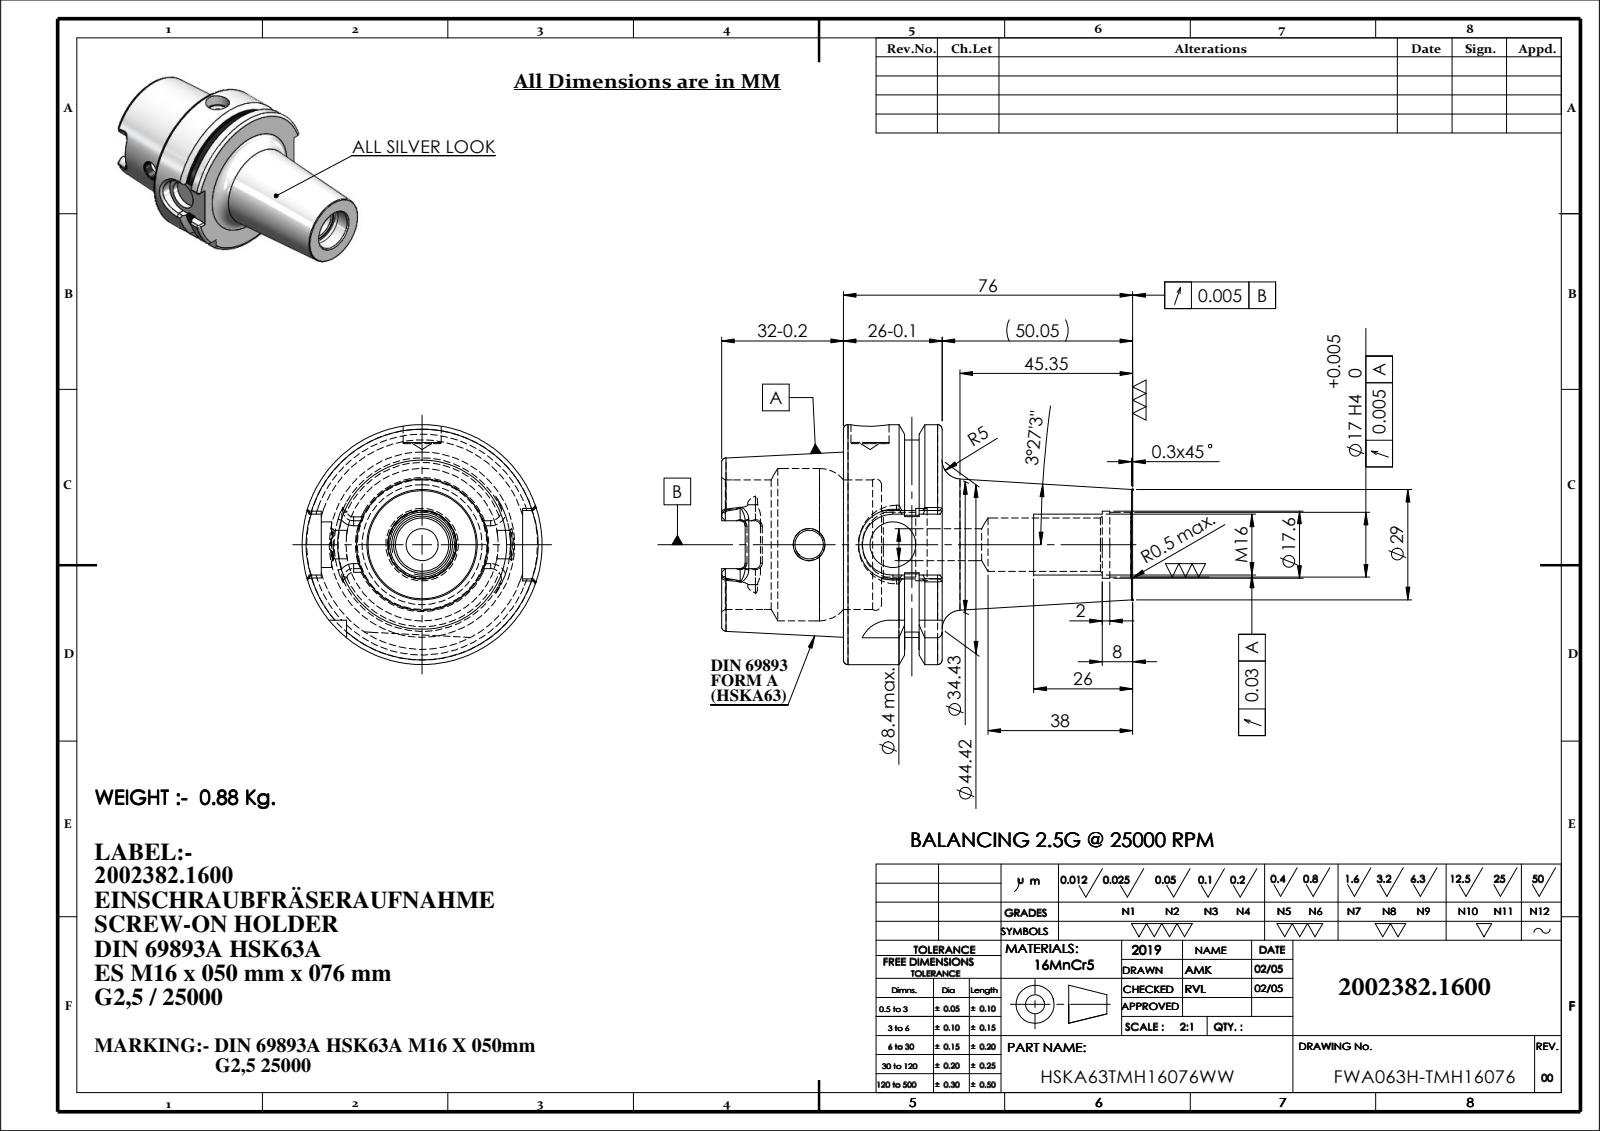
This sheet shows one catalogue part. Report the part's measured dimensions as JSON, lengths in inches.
{"part_name": "9163a-es8m16050", "step_written_by": "SolidWorks 2018 (AUTOMOTIVE_DESIGN)", "units": "inches", "bodies": {"solids": 1, "faces": 170, "planar": 51, "cylindrical": 51, "other": 68}, "overall_size": [4.252, 2.48, 2.48], "volume_in3": 6.905, "surface_area_in2": 44.77, "round_holes": [[0.315, 2], [0.295, 1], [0.331, 1], [0.394, 1], [0.551, 1], [0.669, 1], [0.693, 1], [0.748, 1], [1.339, 1], [1.575, 1]], "round_bosses_or_shafts": [[2.48, 1], [2.165, 1]], "partial_cylinders_radius": [[0.051, 6], [0.113, 4], [0.315, 2], [0.354, 1]], "face_to_face_distances": [1.022, 0.394, 0.628, 2.126, 1.26, 1.654, 2.281, 4.252, 2.992, 2.598]}
